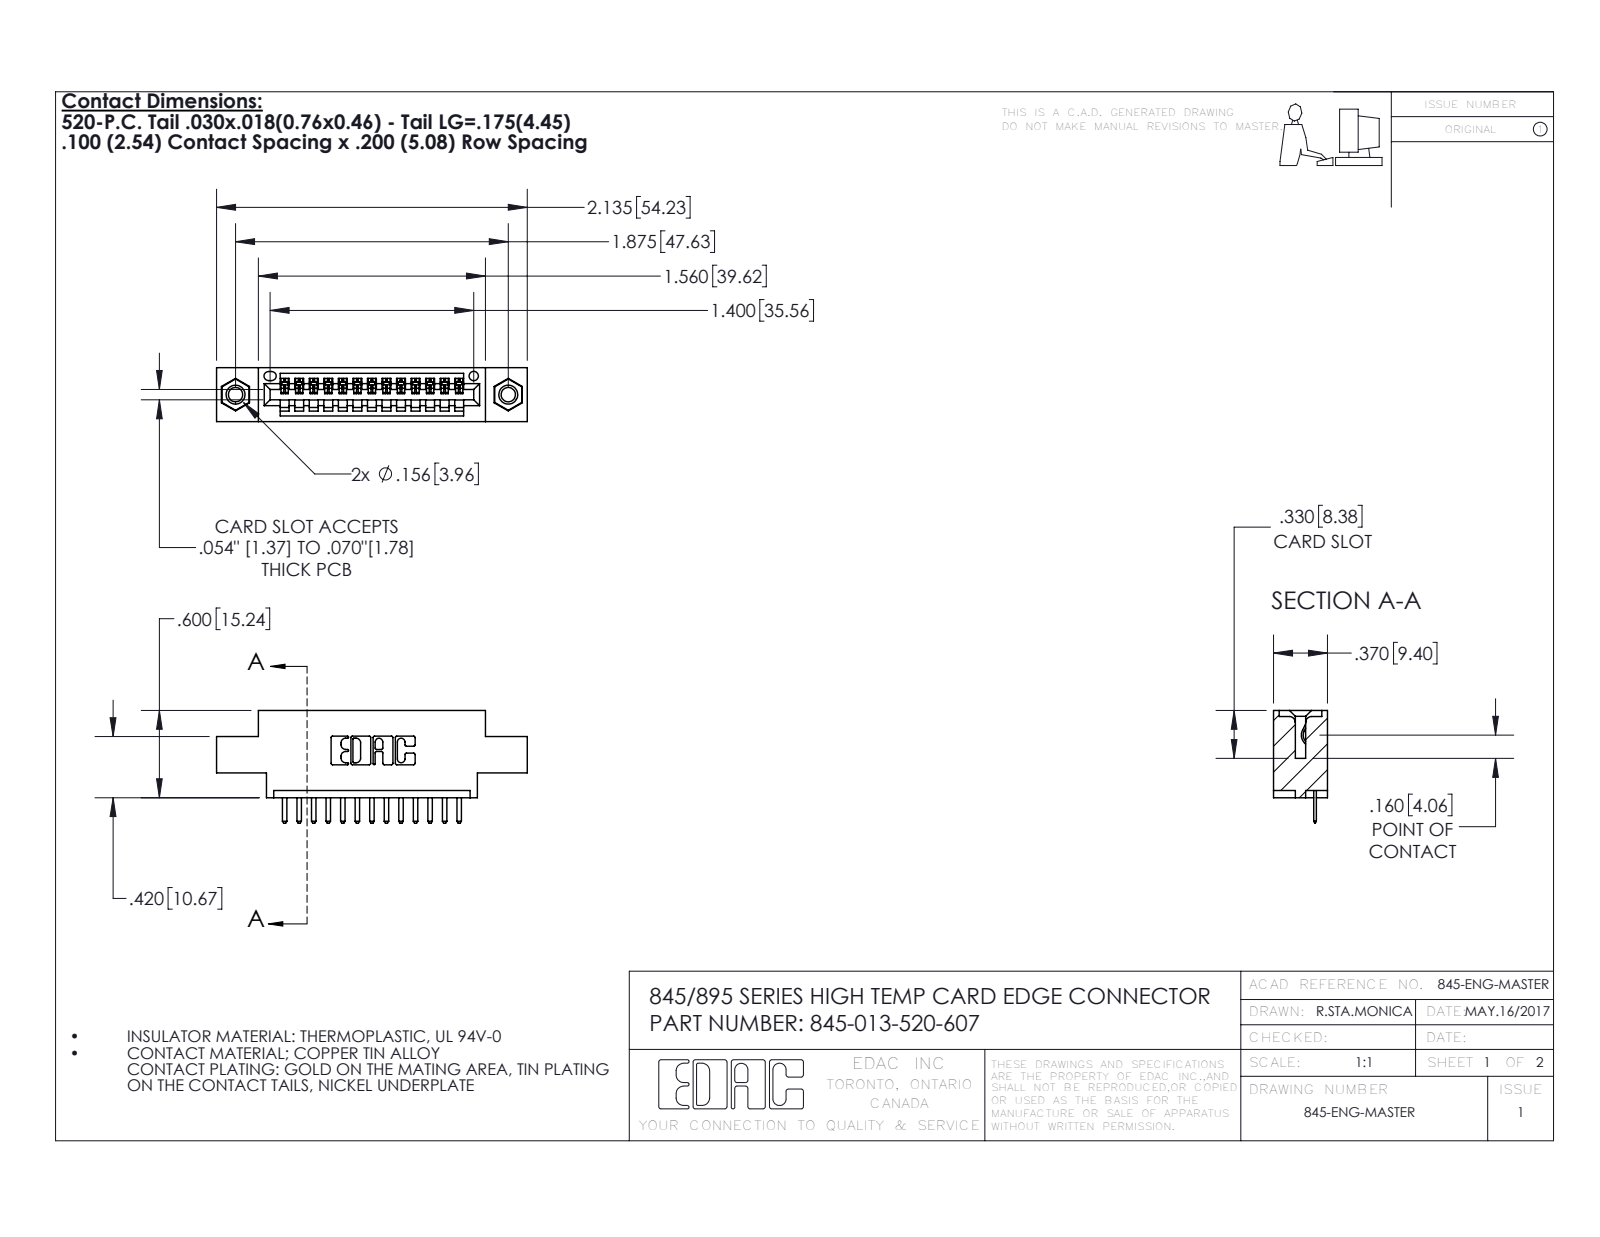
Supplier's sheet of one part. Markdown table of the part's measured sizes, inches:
| quantity | value |
| --- | --- |
| part name | 345-292-001_345-293-120; 345 Part_0.170 Offset - 0.156 Dia-TI; 345-013-520-607; 345-250-001_345-250-005-103 |
| STEP written by | SolidWorks 2016 (CONFIG_CONTROL_DESIGN) |
| units | inches |
| bodies | 16 solids, 996 faces (662 planar, 318 cylindrical, 16 other) |
| overall size | 2.135 × 0.775 × 0.37 |
| volume | 0.29 in³ |
| surface area | 9.228 in² |
| round holes (diameter × count) | 0.098 × 2, 0.125 × 2, 0.156 × 2, 0.064 × 1 |
| round bosses / shafts (diameter × count) | 0.155 × 2 |
| partial cylindrical surfaces (radius × count) | 0.01 × 28, 0.006 × 26, 0.01 × 22, 0.007 × 6, 0.031 × 6, 0.026 × 3, 0.031 × 2, 0.04 × 2 |
| main face-to-face distances | 0.37, 0.072, 0.298, 0.2, 0.098, 0.272, 0.025, 0.1, 0.225, 0.15 |
| hole center spacings | 0.27, 1.643, 1.875 |
